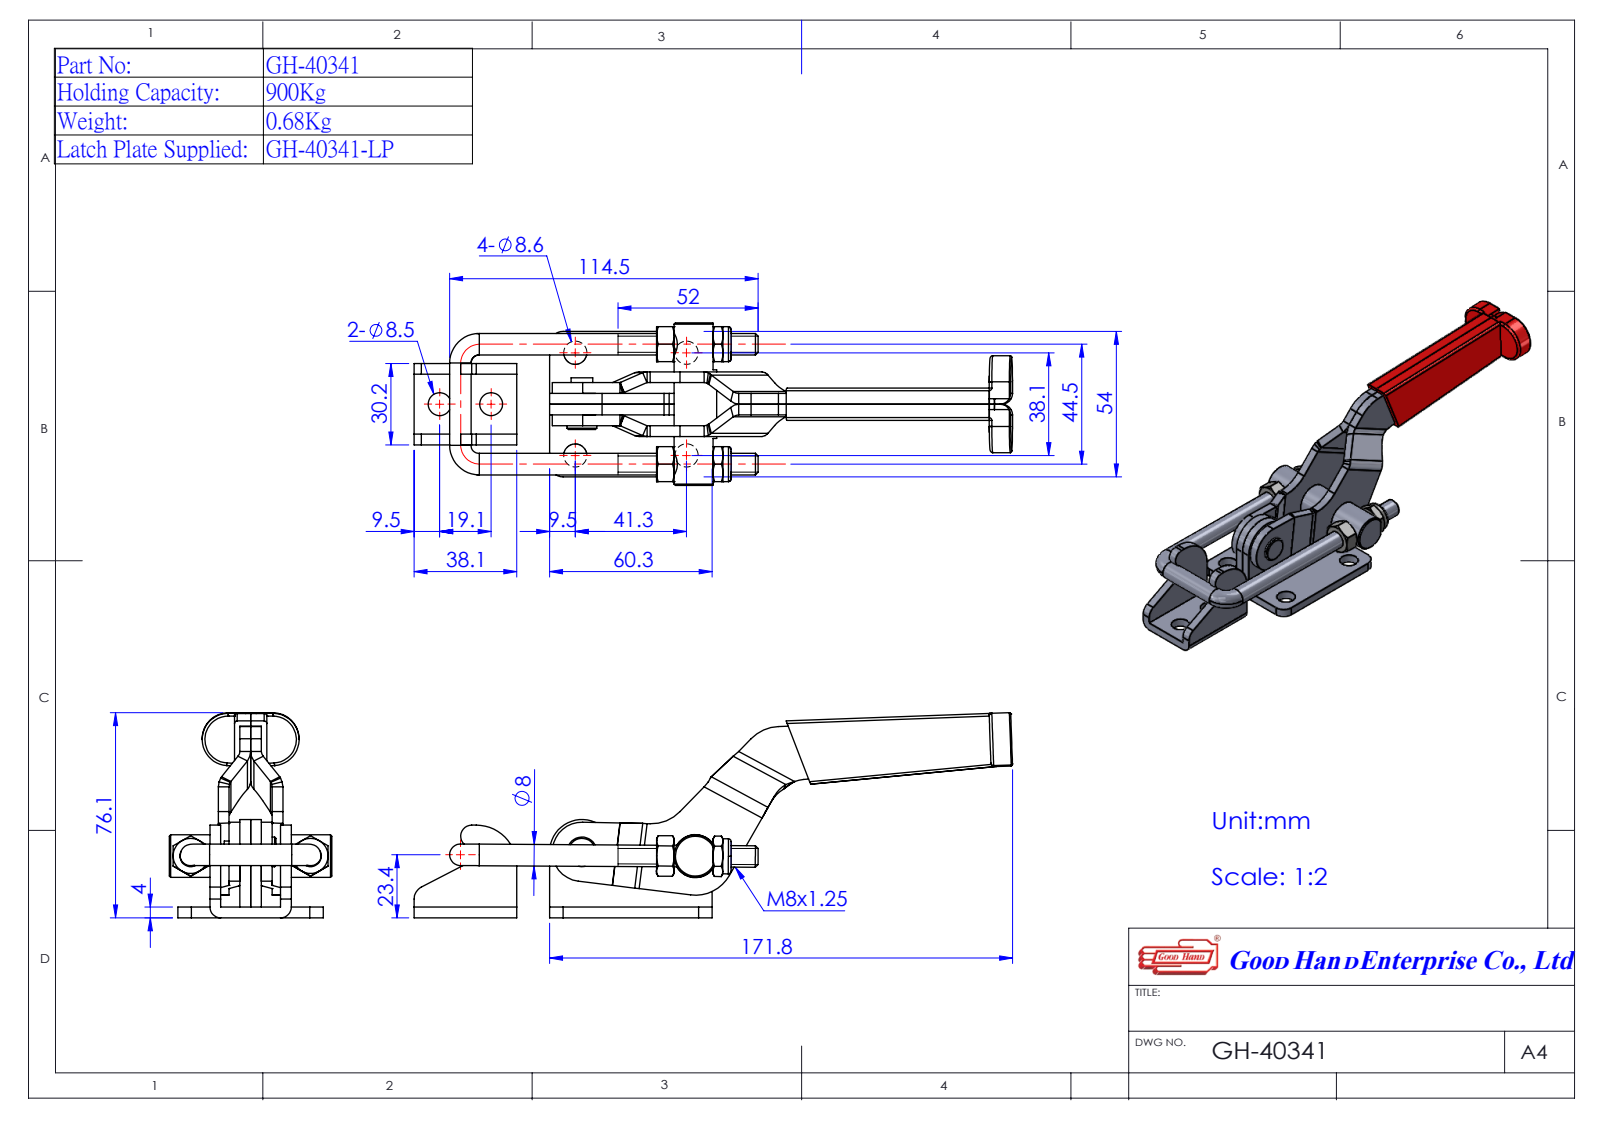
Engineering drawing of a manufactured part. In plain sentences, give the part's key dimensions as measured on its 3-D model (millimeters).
The part is named "493798(GH-40341); Group3^493798(GH-40341); Group4^493798(GH-40341); Group1^493798(GH-40341) (+1 more)". Its 3-D file was written by "SolidWorks 2016 (AUTOMOTIVE_DESIGN)". It is 6 solids with 342 faces: 162 planar, 112 cylindrical and 68 other. Overall it measures 230.32 by 76.14 by 60.3 millimeters. Its volume is 103 216 cubic millimeters and its surface area 47 081 square millimeters. Round holes: 4 of diameter 8, 4 of diameter 8.6, 2 of diameter 6.8, 2 of diameter 8.5, 2 of diameter 9.43, 1 of diameter 6, 1 of diameter 15. Round bosses or shafts: 4 of diameter 8, 2 of diameter 13, 1 of diameter 15.8, 1 of diameter 11. Partial cylindrical surfaces (rounded edges, fillets, slot ends): 9 of radius 5, 6 of radius 15, 4 of radius 0.1, 4 of radius 4.1, 4 of radius 9, 2 of radius 9.71, 1 of radius 3, 1 of radius 4. The main face-to-face distances are 4, 2, 12, 8, 16, 3.1, 7.1, 19.1, 23.1, 10. The hole center spacings are 44.5, 38.1, 41.3, 43.72, 56.19, 61.48, 82.87, 101.55.
